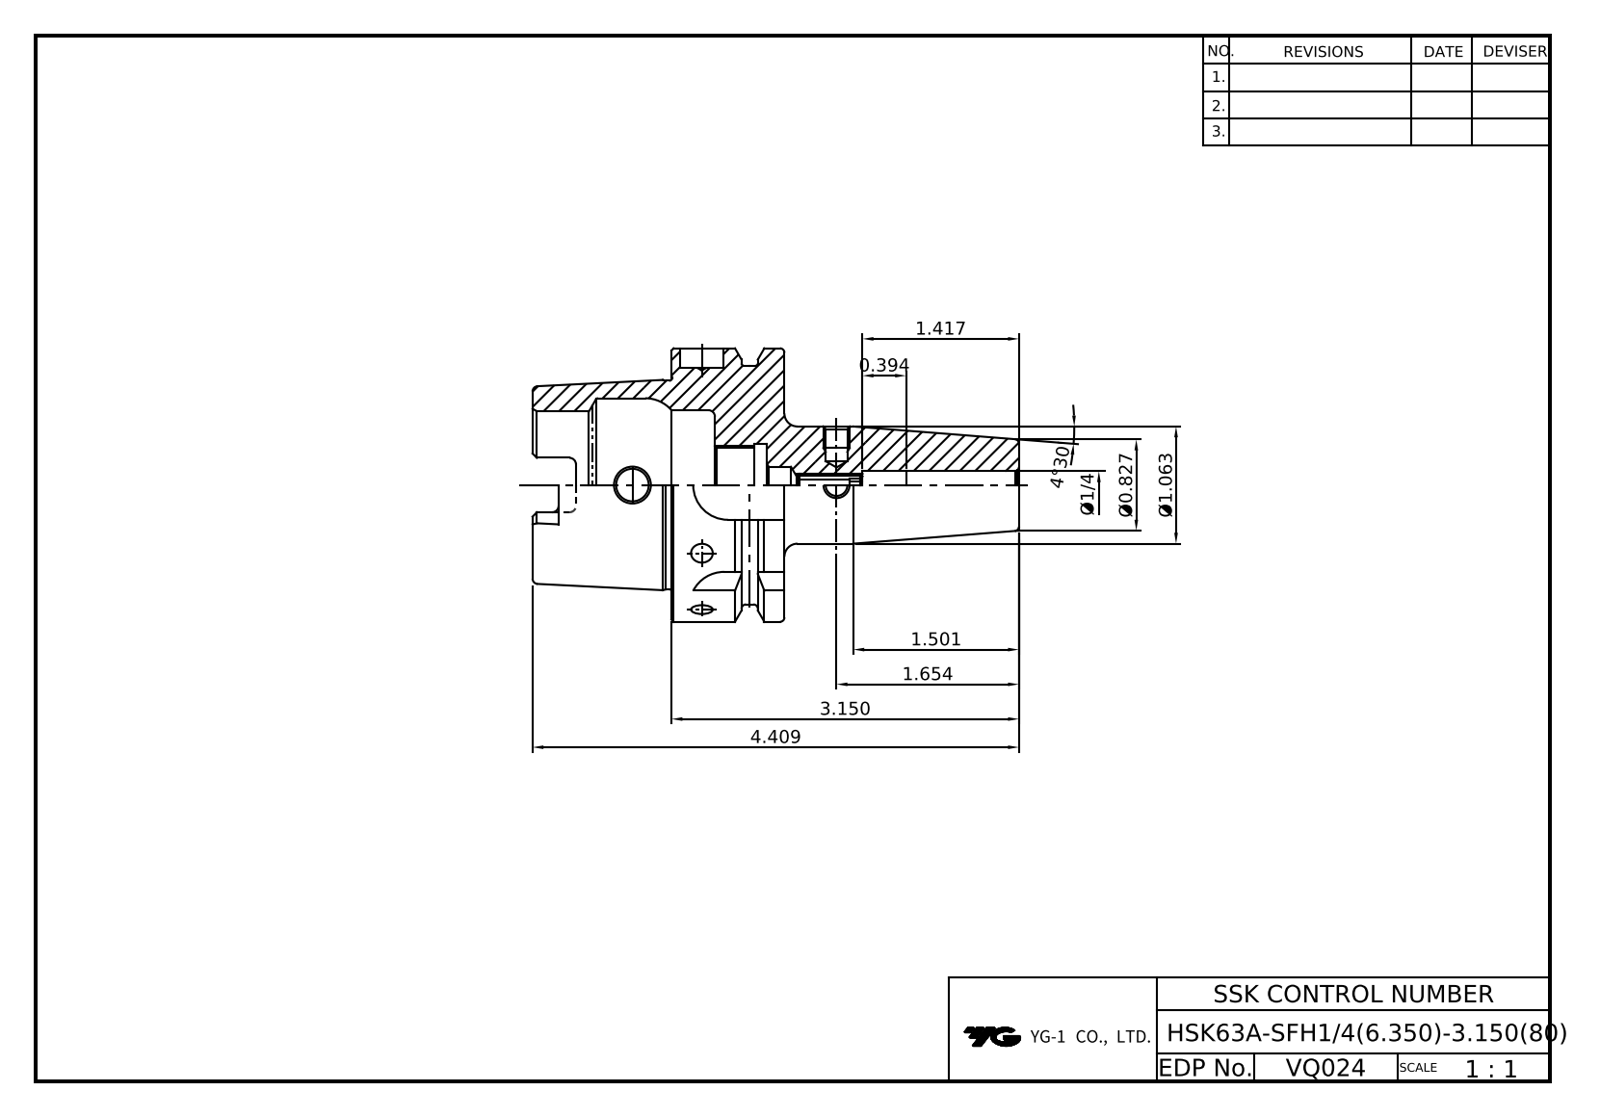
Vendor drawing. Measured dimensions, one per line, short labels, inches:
name: VQ024-HSK63A-SFH0_25-3_15
written by: PRO/ENGINEER BY PARAMETRIC TECHNOLOGY CORPORATION, 2012130 (CONFIG_CONTROL_DESIGN)
unit: in
bodies: 1 solid, 202 faces (57 planar, 59 cylindrical, 86 other)
size: 4.41 × 2.48 × 2.48
volume: 6.459 in³; area: 43.78 in²
holes: 2× ⌀0.197, 1× ⌀0.166, 1× ⌀0.25, 1× ⌀0.266, 1× ⌀0.295, 1× ⌀0.33, 1× ⌀0.394, 1× ⌀0.669, 1× ⌀0.709, 1× ⌀0.748, 1× ⌀1.339, 1× ⌀1.358
bosses: 1× ⌀2.48, 1× ⌀2.165, 1× ⌀1.891, 1× ⌀1.063
rounds: 6× R0.059, 4× R0.113, 4× R0.315
face distances: 1.024, 0.394, 0.63, 1.26, 1.654, 2.283, 2.087, 0.157, 0.866, 4.41
hole spacings: 1.22, 1.85
